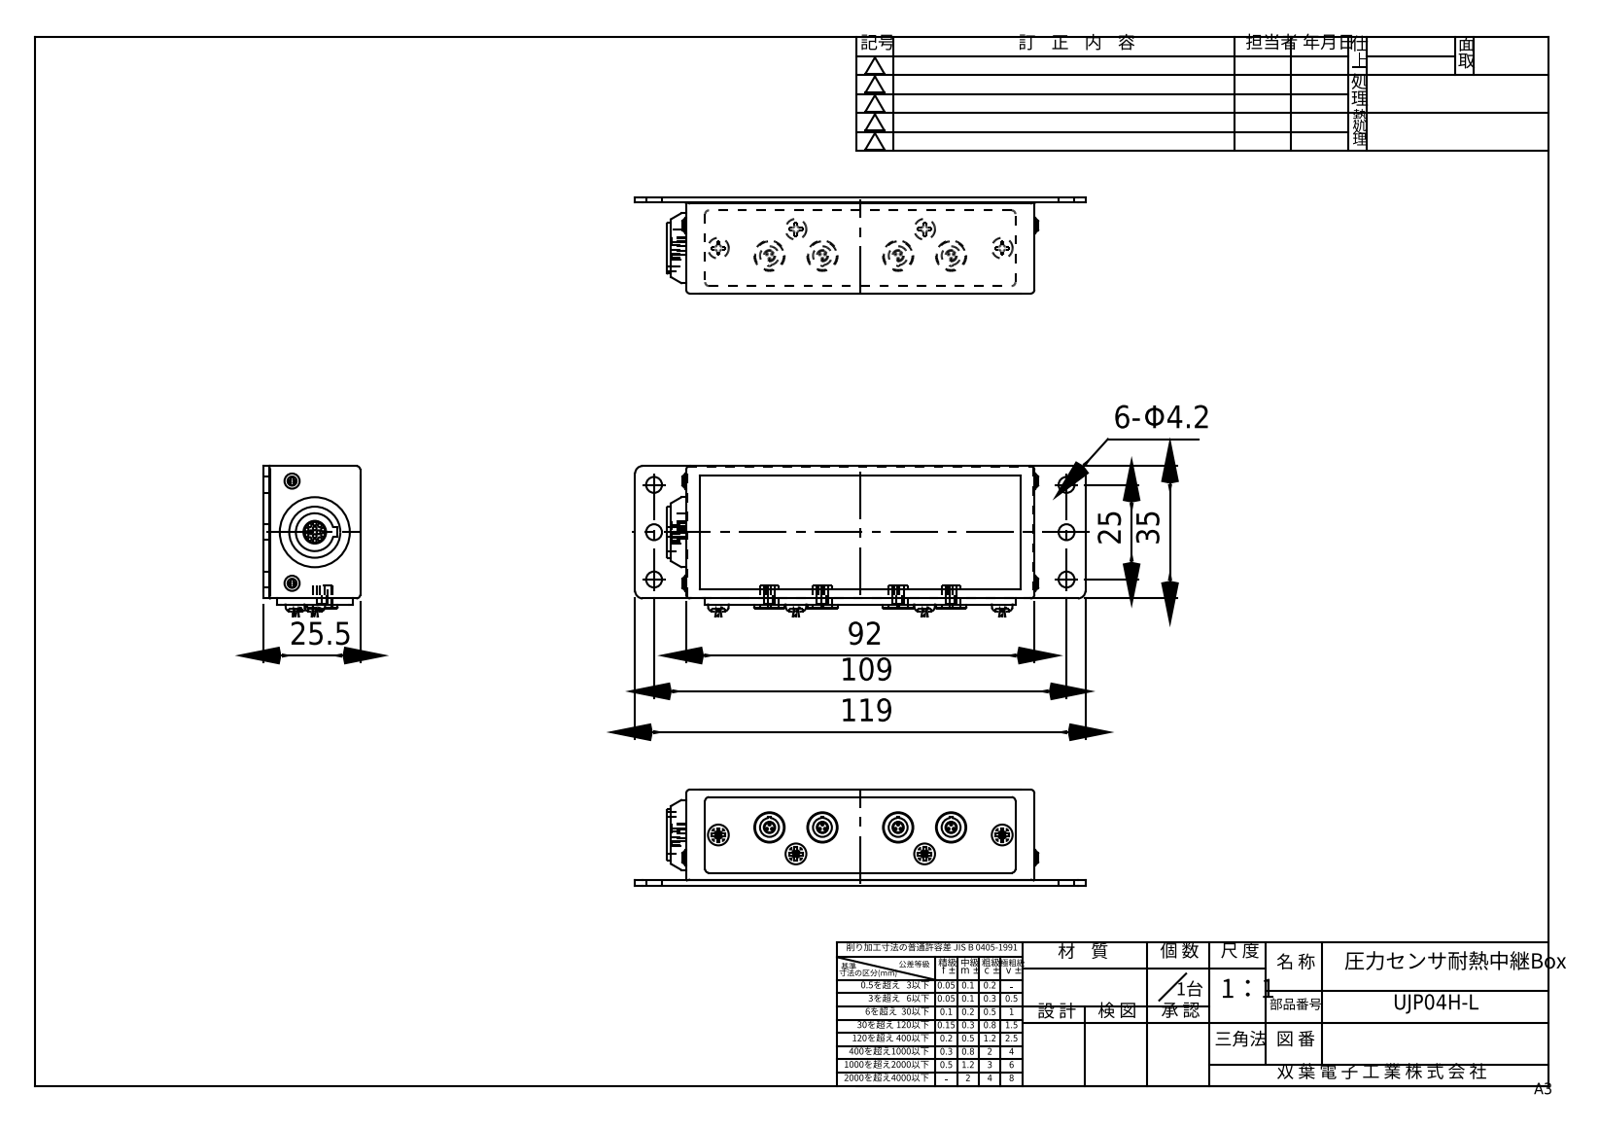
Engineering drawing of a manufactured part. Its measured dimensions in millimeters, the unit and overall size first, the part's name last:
Units: millimetres
Overall size (bounding box): 119 × 38.56 × 25.6
Round holes (diameter × count): ⌀1 ×14, ⌀0.6 ×12, ⌀4.2 ×6, ⌀5 ×4, ⌀10 ×1
Round bosses / shafts (diameter × count): ⌀8 ×4, ⌀3 ×4, ⌀4 ×2, ⌀18.5 ×1, ⌀13.5 ×1, ⌀6 ×1
Partial cylindrical surfaces — rounded edges, fillets, slot ends (radius × count): R0.55 ×16, R1 ×12, R0.2 ×8, R2 ×4, R2.75 ×4
Main face-to-face distances: 25.6, 36.6, 1.5, 24.1, 1.6, 35, 92, 25.5, 24, 2
Hole centre spacings: 0.8, 1.38, 2.25, 3.64, 4.28, 1.39, 14, 34
Volume: 86 971 mm³ · Surface area: 16 652 mm²
Bodies: 1 solid, 323 faces (186 planar, 104 cylindrical, 33 other)
STEP written by: XStep 1.0 (automotive_design)
